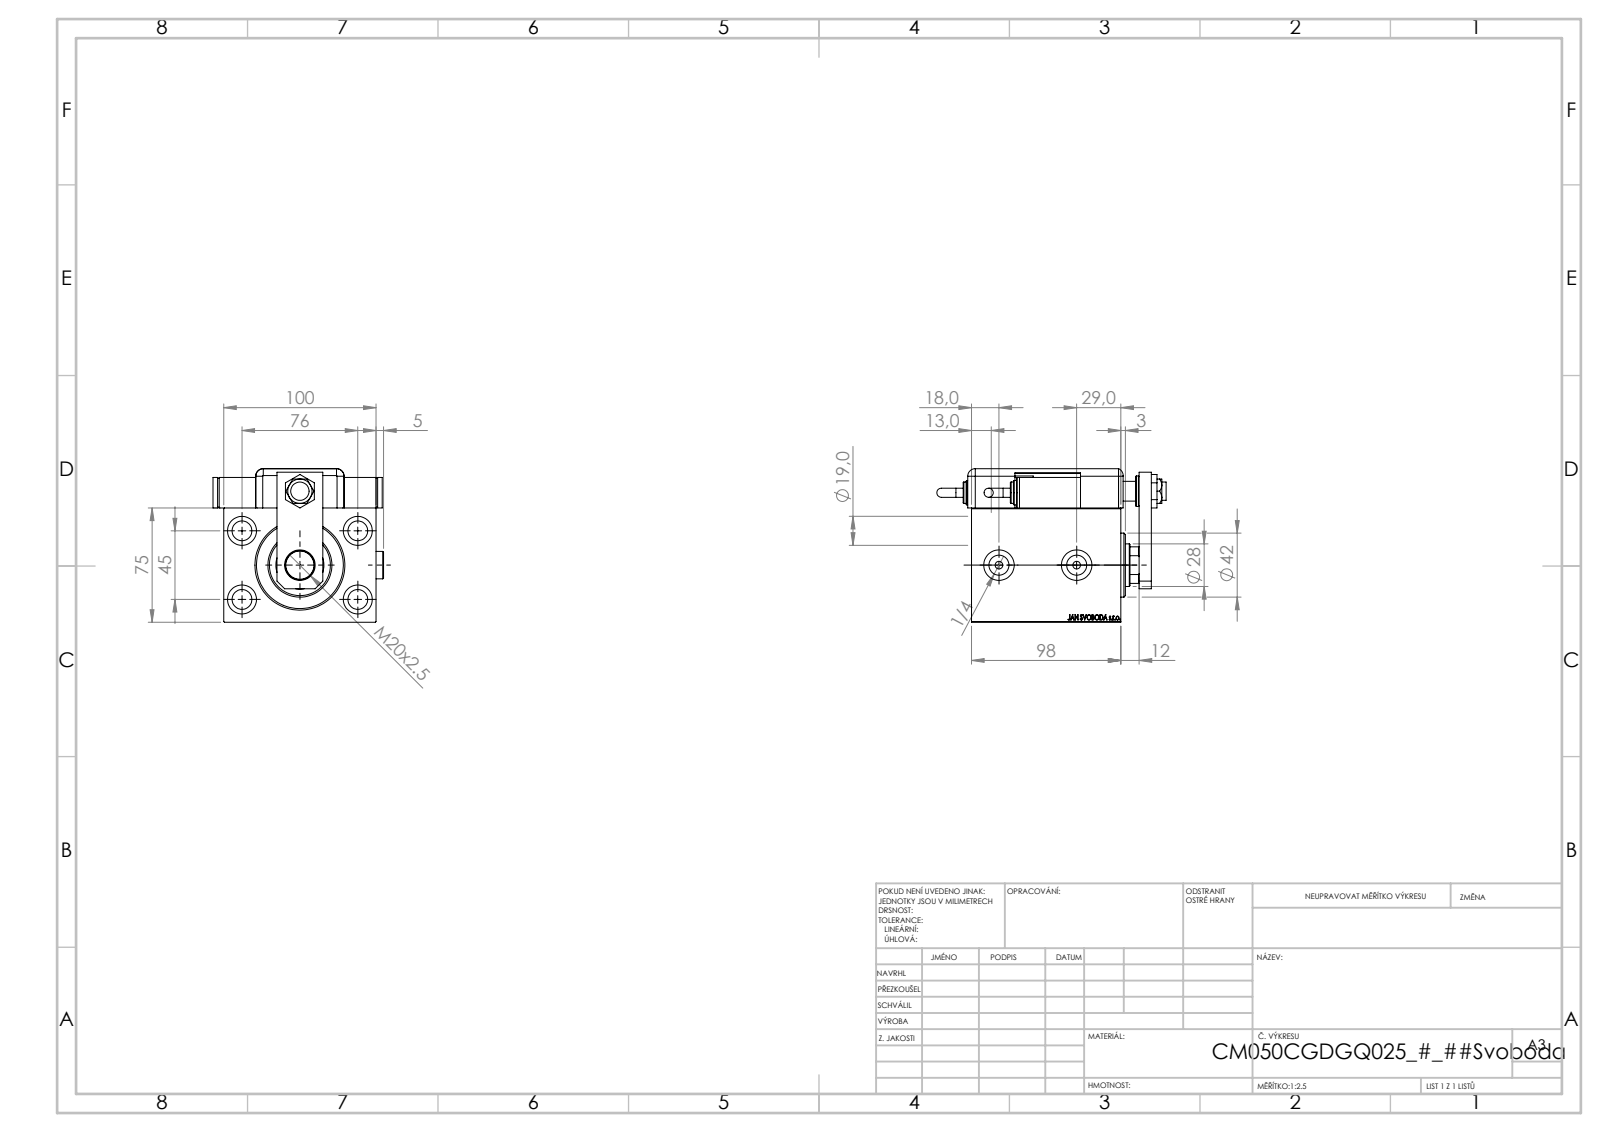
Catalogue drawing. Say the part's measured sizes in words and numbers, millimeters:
The part is named "SWITCH_Q_FRONT_BACK; MAGNETIC SWITCH Q; SWITCH Q; SWITCH DIM A_G (+8 more)". Its 3-D file was written by "SolidWorks 2019 (CONFIG_CONTROL_DESIGN)". It is 15 solids with 1303 faces: 649 planar, 133 cylindrical and 521 other. Overall it measures 150.46 by 111.9 by 100.8 millimeters. Its volume is 770 831 cubic millimeters and its surface area 162 779 square millimeters. Round holes: 5 of diameter 13, 4 of diameter 19, 3 of diameter 20, 2 of diameter 4, 2 of diameter 5, 2 of diameter 8, 2 of diameter 13.16, 1 of diameter 12, 1 of diameter 14, 1 of diameter 18.5, 1 of diameter 28, 1 of diameter 31.5. Round bosses or shafts: 3 of diameter 20, 2 of diameter 18, 2 of diameter 16, 2 of diameter 14, 2 of diameter 6, 1 of diameter 42. Partial cylindrical surfaces (rounded edges, fillets, slot ends): 9 of radius 5, 1 of radius 10, 1 of radius 13.5. The main face-to-face distances are 75, 3, 100, 98, 14, 20, 13.5, 84, 25.8, 100.8. The hole center spacings are 44.16, 45, 46.04, 76, 80.53, 88.32, 20, 48.5.
